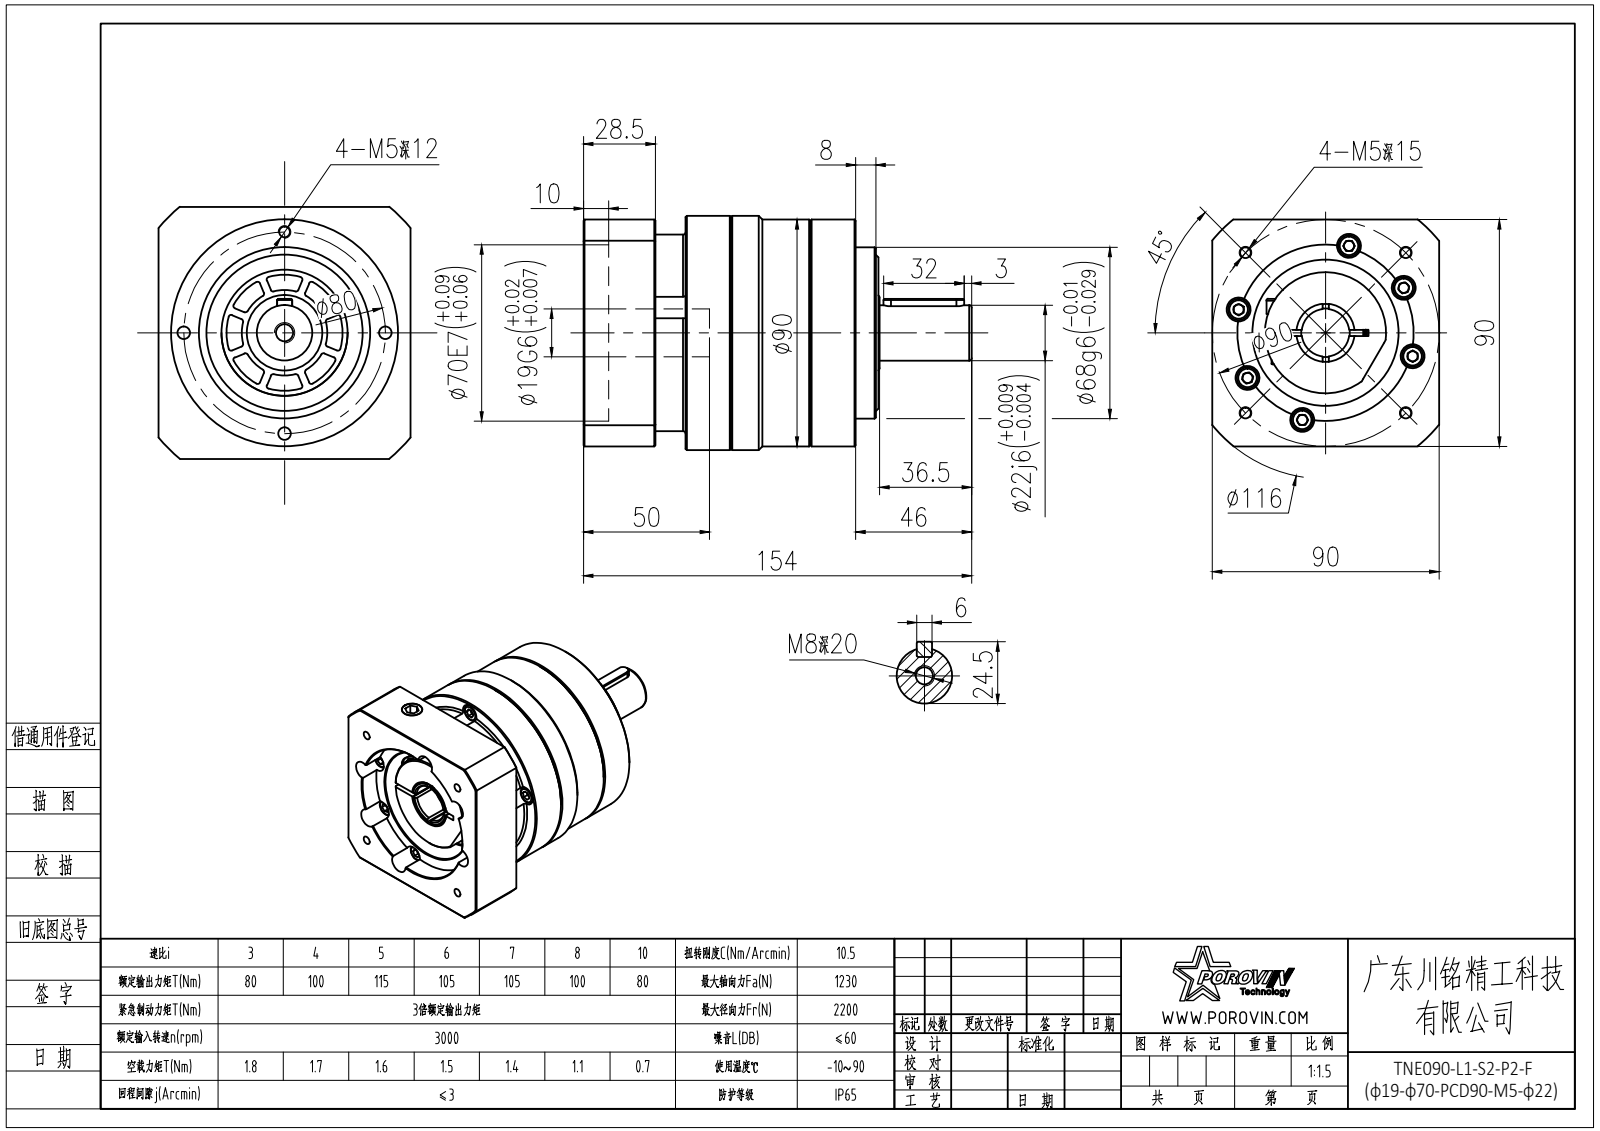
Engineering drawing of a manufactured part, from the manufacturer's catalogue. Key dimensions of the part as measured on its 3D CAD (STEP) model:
Part name (STEP PRODUCT): spring lock washers--normal type gb_GB_FASTENER_WASHER_SW 5; hexagon socket head cap screws gb_GB_FASTENER_SCREWS_HSHCS M5X20-N; 一级齿圈外形图 KE90; hex socket set screws with flat point gb_GB_FASTENER_SCREWS_HSFP M12X12-N (+1 more)
STEP written by: SolidWorks 2016 (CONFIG_CONTROL_DESIGN)
Units: millimetres
Bodies: 29 solids, 842 faces (335 planar, 315 cylindrical, 192 other)
Overall size (bounding box): 154 × 93 × 93
Volume: 652 910 mm³ · Surface area: 128 794 mm²
Round holes (diameter × count): ⌀4.2 ×10, ⌀5.4 ×10, ⌀5.5 ×10, ⌀9.5 ×10, ⌀5 ×5, ⌀6.5 ×1, ⌀6.8 ×1, ⌀8.5 ×1, ⌀10.2 ×1, ⌀19 ×1, ⌀19.2 ×1, ⌀50 ×1
Round bosses / shafts (diameter × count): ⌀8.5 ×10, ⌀8 ×10, ⌀5 ×10, ⌀93 ×1, ⌀90 ×1, ⌀78.5 ×1, ⌀78 ×1, ⌀68 ×1
Partial cylindrical surfaces — rounded edges, fillets, slot ends (radius × count): R1 ×32, R3 ×2, R5.5 ×1, R23 ×1, R35 ×1, R58 ×1
Main face-to-face distances: 31.5, 90, 58.5, 32.5, 64, 2.5, 18, 26, 49.5, 28.5
Hole centre spacings: 32.85, 78.55, 35.75, 75.85, 10.75, 22.73, 33.05, 40
